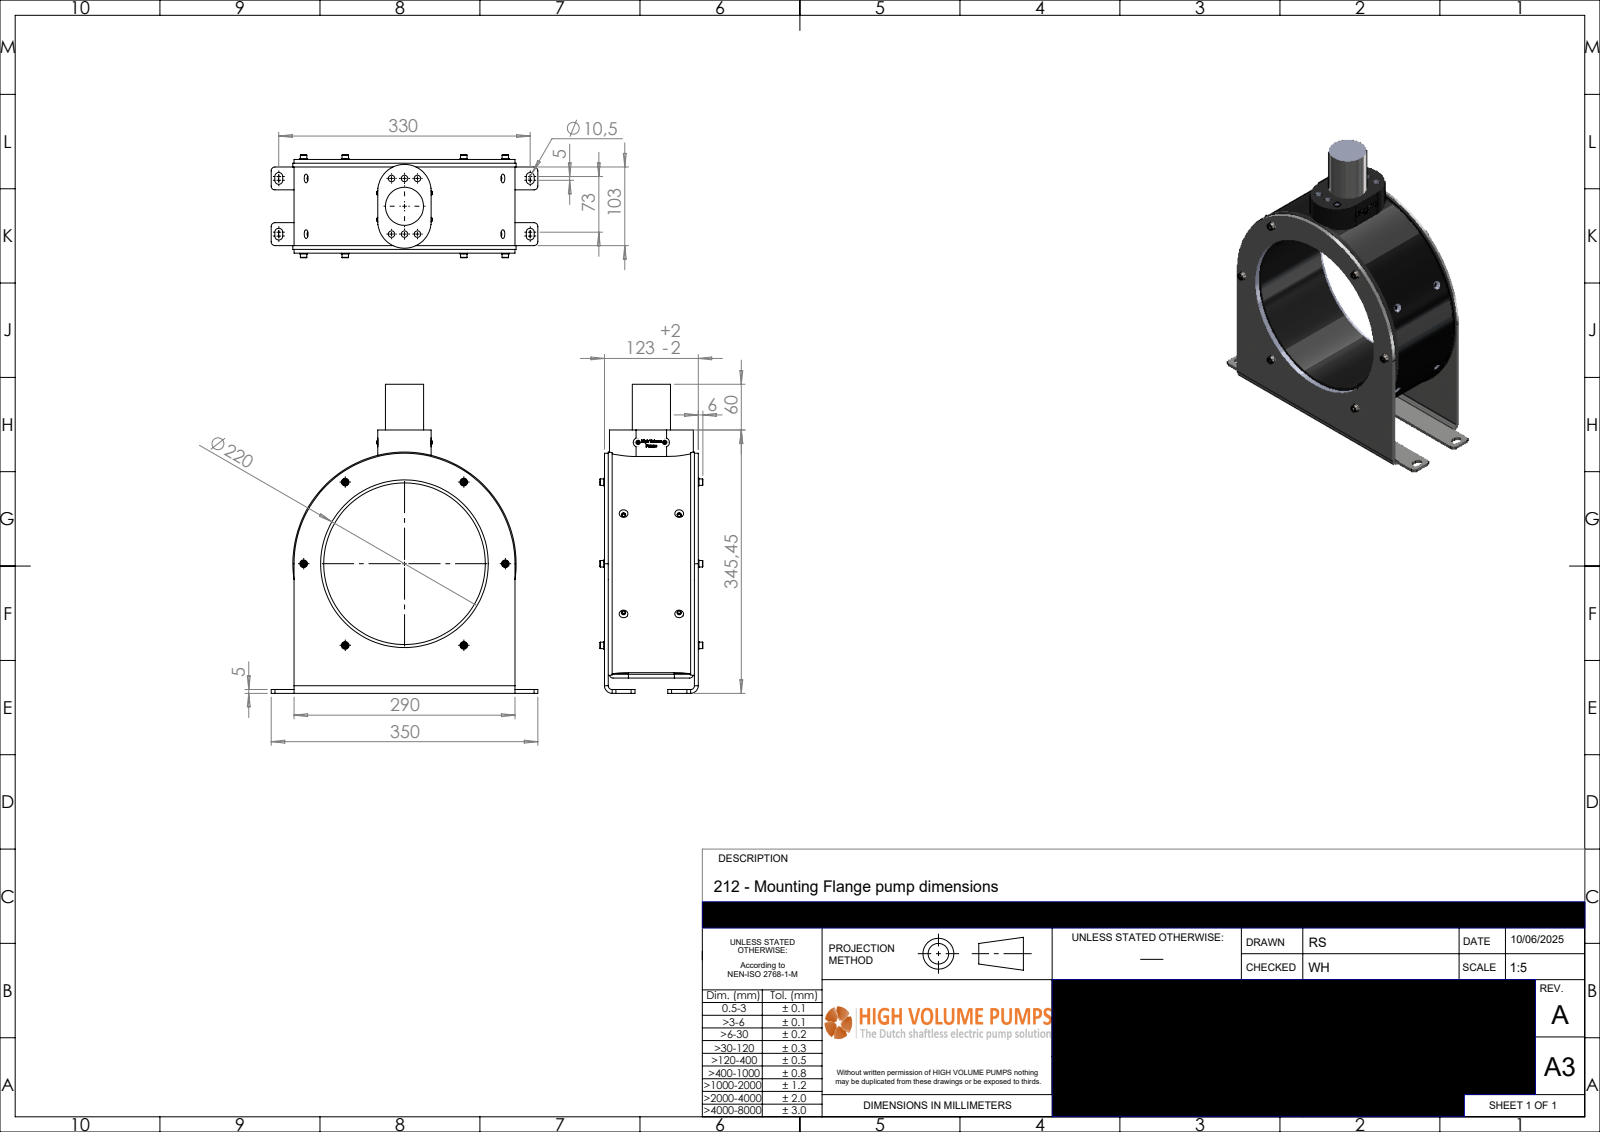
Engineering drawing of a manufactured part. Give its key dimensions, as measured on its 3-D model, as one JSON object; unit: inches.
{"part_name": "P-212-030-rev-A-MF", "step_written_by": "SolidWorks 2024 (AUTOMOTIVE_DESIGN)", "units": "inches", "bodies": {"solids": 1, "faces": 941, "planar": 559, "cylindrical": 116, "other": 266}, "overall_size": [15.963, 13.78, 5.317], "volume_in3": 267.3, "surface_area_in2": 619, "round_holes": [[0.22, 6], [0.335, 6], [0.165, 4], [0.217, 4], [8.346, 1], [8.661, 1]], "round_bosses_or_shafts": [[0.394, 6], [0.335, 6], [0.197, 6], [0.38, 2], [0.224, 2], [11.535, 1], [11.417, 1], [1.969, 1]], "partial_cylinders_radius": [[0.197, 12], [0.207, 8], [0.984, 4], [0.079, 2], [0.246, 2], [0.394, 2], [1.378, 2], [0.039, 1]], "face_to_face_distances": [0.197, 4.845, 4.648, 4.451, 4.589, 0.256, 0.059, 4.392, 13.6, 13.404], "hole_center_spacings": [2.874, 0.669, 2.951, 4.732, 5.211, 9.287, 1.339, 3.17]}
